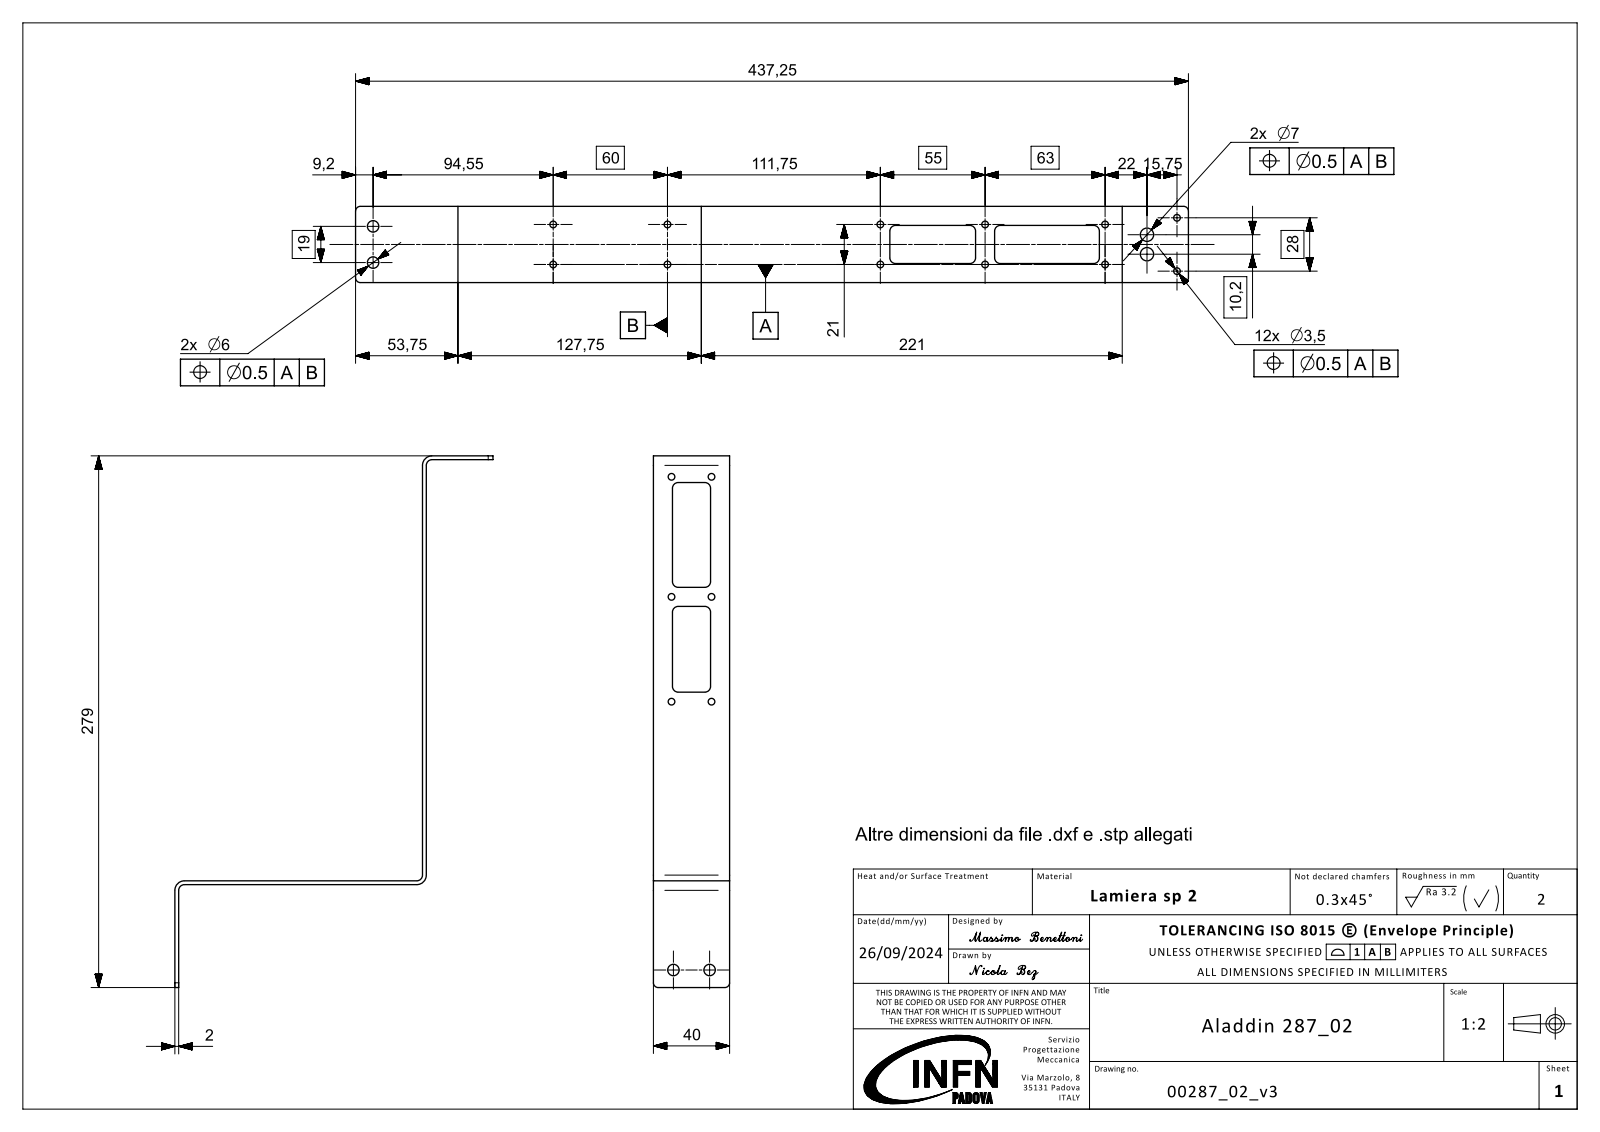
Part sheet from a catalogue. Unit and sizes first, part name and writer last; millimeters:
Units: millimetres
Overall size (bounding box): 279 × 167 × 40
Round holes (diameter × count): ⌀3.5 ×12, ⌀6 ×2, ⌀7 ×2
Partial cylindrical surfaces — rounded edges, fillets, slot ends (radius × count): R3 ×11, R2.5 ×4, R5 ×3
Main face-to-face distances: 2, 130, 223, 132, 128, 225, 221, 40, 10, 30
Hole centre spacings: 21, 18.09, 24.76, 33.68, 36.73, 49.12, 54.78, 55
Volume: 30 630 mm³ · Surface area: 33 504 mm²
Bodies: 1 solid, 54 faces (20 planar, 34 cylindrical, 0 other)
Part name (STEP PRODUCT): 00287_02_v3_objects
STEP written by: SIEMENS PLM Software NX2306.9102 (AUTOMOTIVE_DESIGN)
